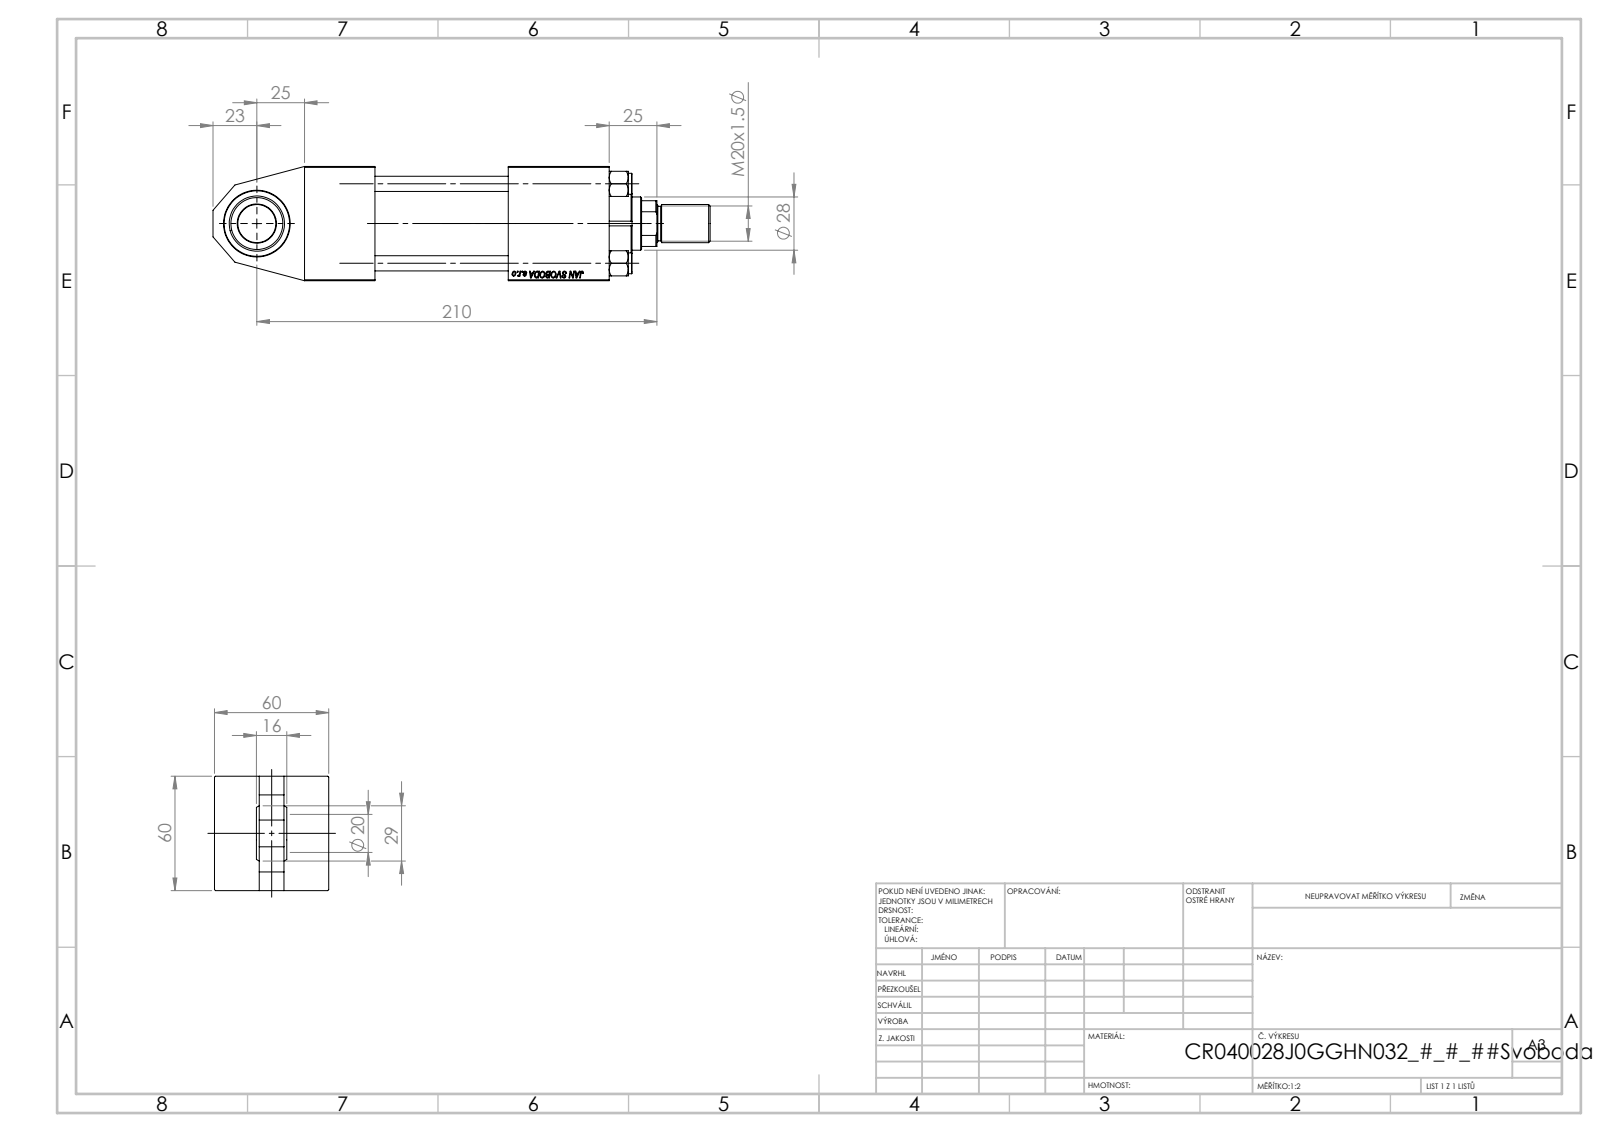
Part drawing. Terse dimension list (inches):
name: ROD_END_AH; V215CR_TYCINKA_J; V215CR_J_Body; NUT_M5_J (+3 more)
written by: SolidWorks 2019 (CONFIG_CONTROL_DESIGN)
unit: in
bodies: 13 solids, 1161 faces (523 planar, 92 cylindrical, 546 other)
size: 10.276 × 2.362 × 2.362
volume: 28.95 in³; area: 199.4 in²
holes: 4× ⌀0.315, 2× ⌀0.098, 2× ⌀0.276, 2× ⌀0.656, 2× ⌀0.945, 1× ⌀0.728, 1× ⌀0.787, 1× ⌀1.102, 1× ⌀1.22, 1× ⌀1.378, 1× ⌀1.575, 1× ⌀1.772
bosses: 4× ⌀0.433, 1× ⌀1.811, 1× ⌀1.654, 1× ⌀0.787, 1× ⌀0.709
rounds: 1× R0.531
face distances: 2.362, 1.437, 0.925, 1.457, 2.087, 2.756, 4.843, 4.213, 0.512, 6.299
hole spacings: 0.821, 1.161, 1.642, 1.832, 0.817, 2.322, 1.634, 4.114
